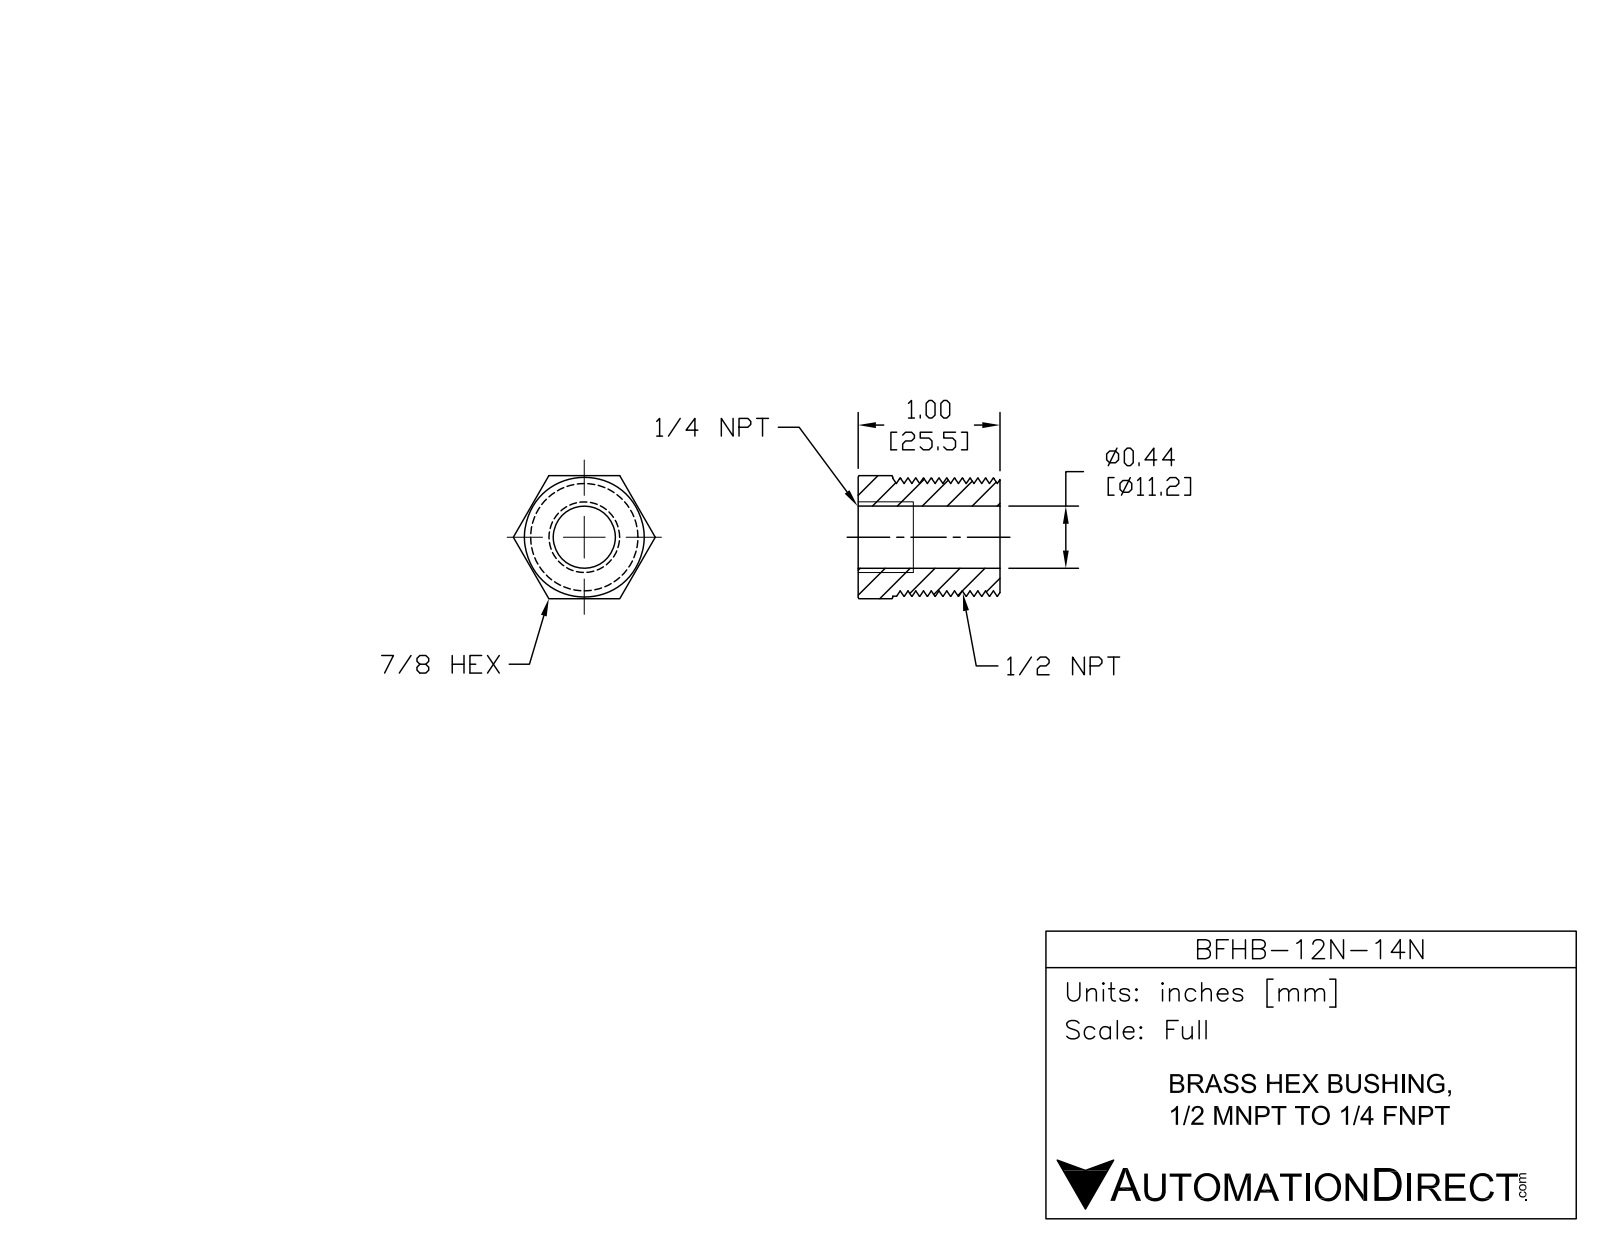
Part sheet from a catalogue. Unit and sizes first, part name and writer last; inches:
Units: inches
Overall size (bounding box): 1.017 × 1.006 × 0.871
Round holes (diameter × count): ⌀0.44 ×1
Round bosses / shafts (diameter × count): ⌀0.836 ×1
Main face-to-face distances: 1.017, 0.871, 0.257, 0.76
Volume: 0.396 in³ · Surface area: 6.353 in²
Bodies: 1 solid, 48 faces (10 planar, 31 cylindrical, 7 other)
Part name (STEP PRODUCT): BFHB-12N-14N
STEP written by: SolidWorks 2015 (CONFIG_CONTROL_DESIGN)
